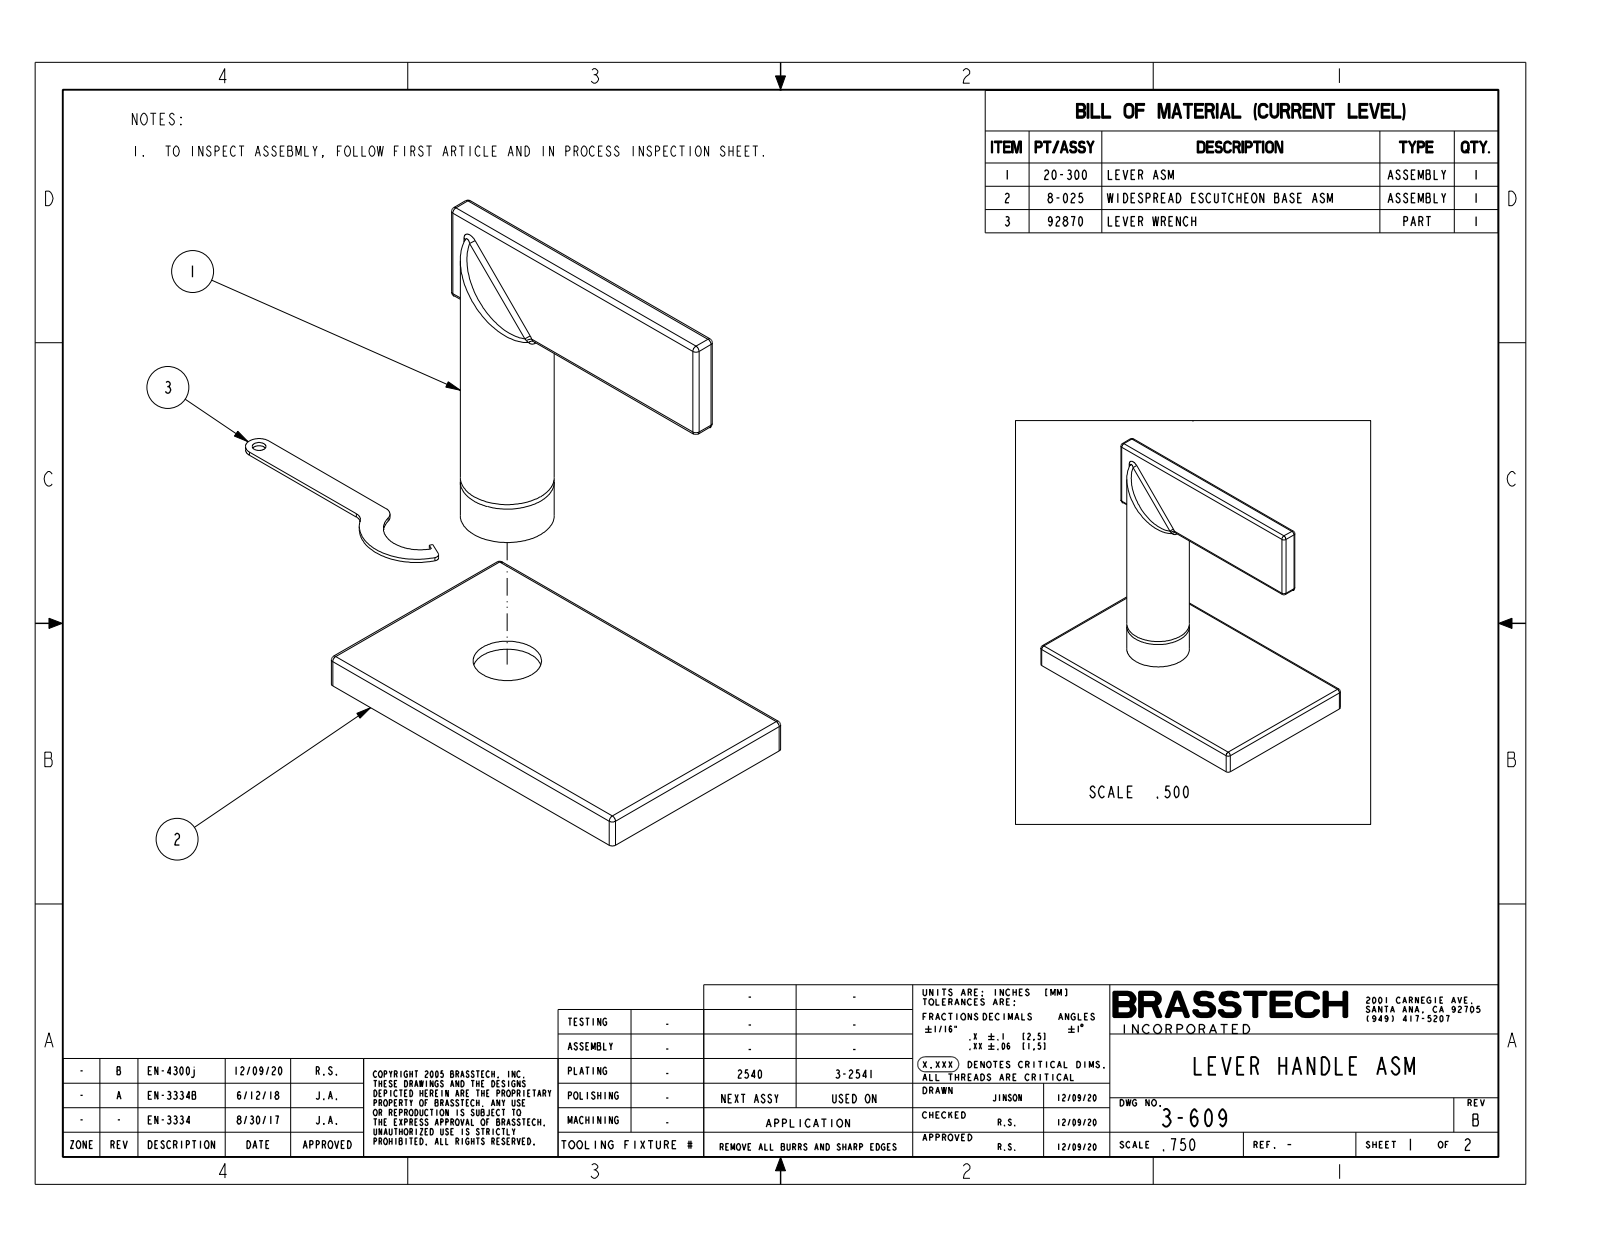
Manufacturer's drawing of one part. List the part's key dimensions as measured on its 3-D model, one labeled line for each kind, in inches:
Part name (STEP PRODUCT): 3-609
STEP written by: CREO PARAMETRIC BY PTC INC, 2018400 (CONFIG_CONTROL_DESIGN)
Units: inches
Bodies: 1 solid, 75 faces (17 planar, 32 cylindrical, 26 other)
Overall size (bounding box): 3.76 × 3.51 × 2.2
Volume: 4.663 in³ · Surface area: 33.74 in²
Round bosses / shafts (diameter × count): ⌀0.86 ×1, ⌀0.68 ×1
Partial cylindrical surfaces — rounded edges, fillets, slot ends (radius × count): R0.04 ×24
Main face-to-face distances: 0.31, 0.236, 0.982, 1.218, 2.2, 3.66, 3.51, 3.2, 2.526, 2.216
